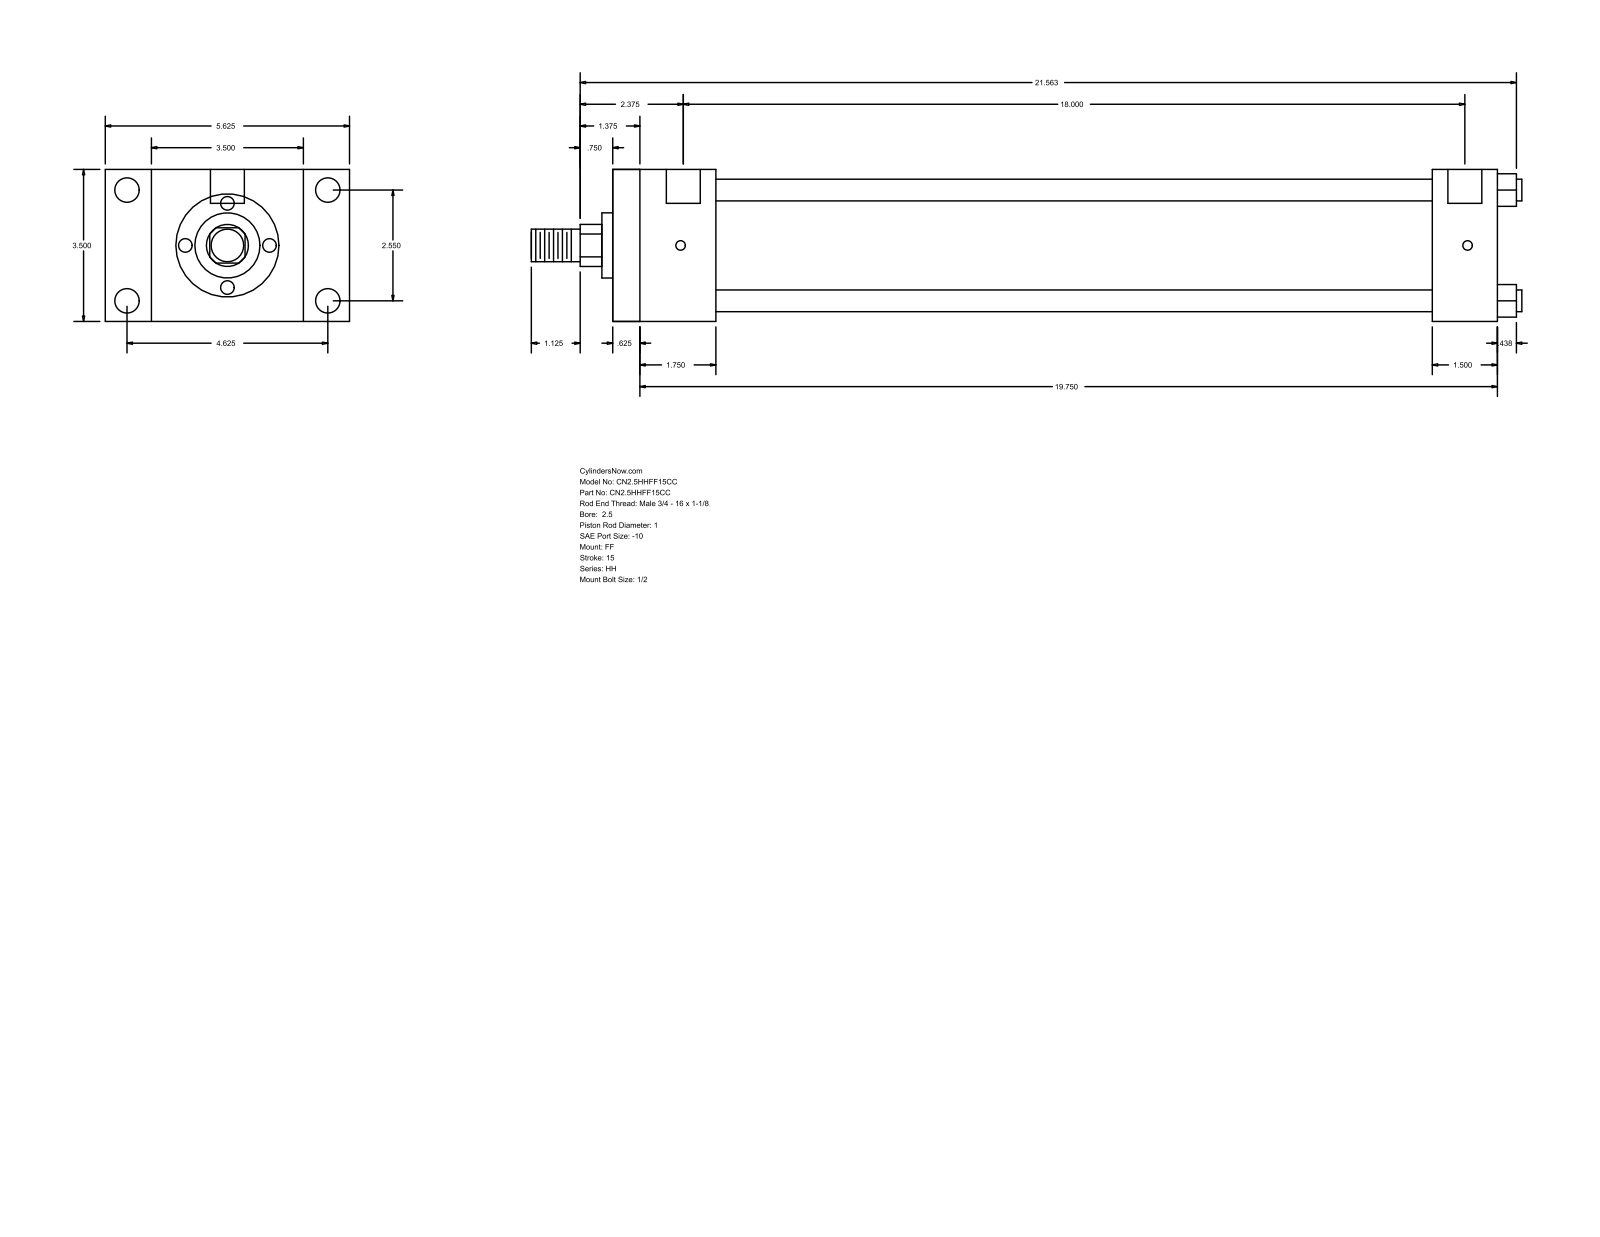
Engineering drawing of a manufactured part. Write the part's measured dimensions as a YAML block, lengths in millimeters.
part_name: "HH_FF__0250_1"
step_written_by: "GSSL Pune (CONFIG_CONTROL_DESIGN)"
units: millimeters
bodies: {solids: 0, faces: 92, planar: 64, cylindrical: 28, other: 0}
overall_size: [579.44, 142.88, 88.9]
round_holes:
  - {diameter: 5.56, count: 4}
  - {diameter: 14.3, count: 4}
  - {diameter: 19.84, count: 2}
round_bosses_or_shafts:
  - {diameter: 12.7, count: 4}
  - {diameter: 73.03, count: 1}
  - {diameter: 38.1, count: 1}
  - {diameter: 25.4, count: 1}
  - {diameter: 19.05, count: 1}
partial_cylinders:
  - {radius: 12.29, count: 1}
face_to_face_distances: [88.9, 517.53, 15.87, 501.66, 38.1, 60.33, 44.46, 457.2, 479.43, 463.56]
hole_center_spacings: [1.59, 64.76, 117.48, 134.15, 458.78, 460.37, 457.19]
